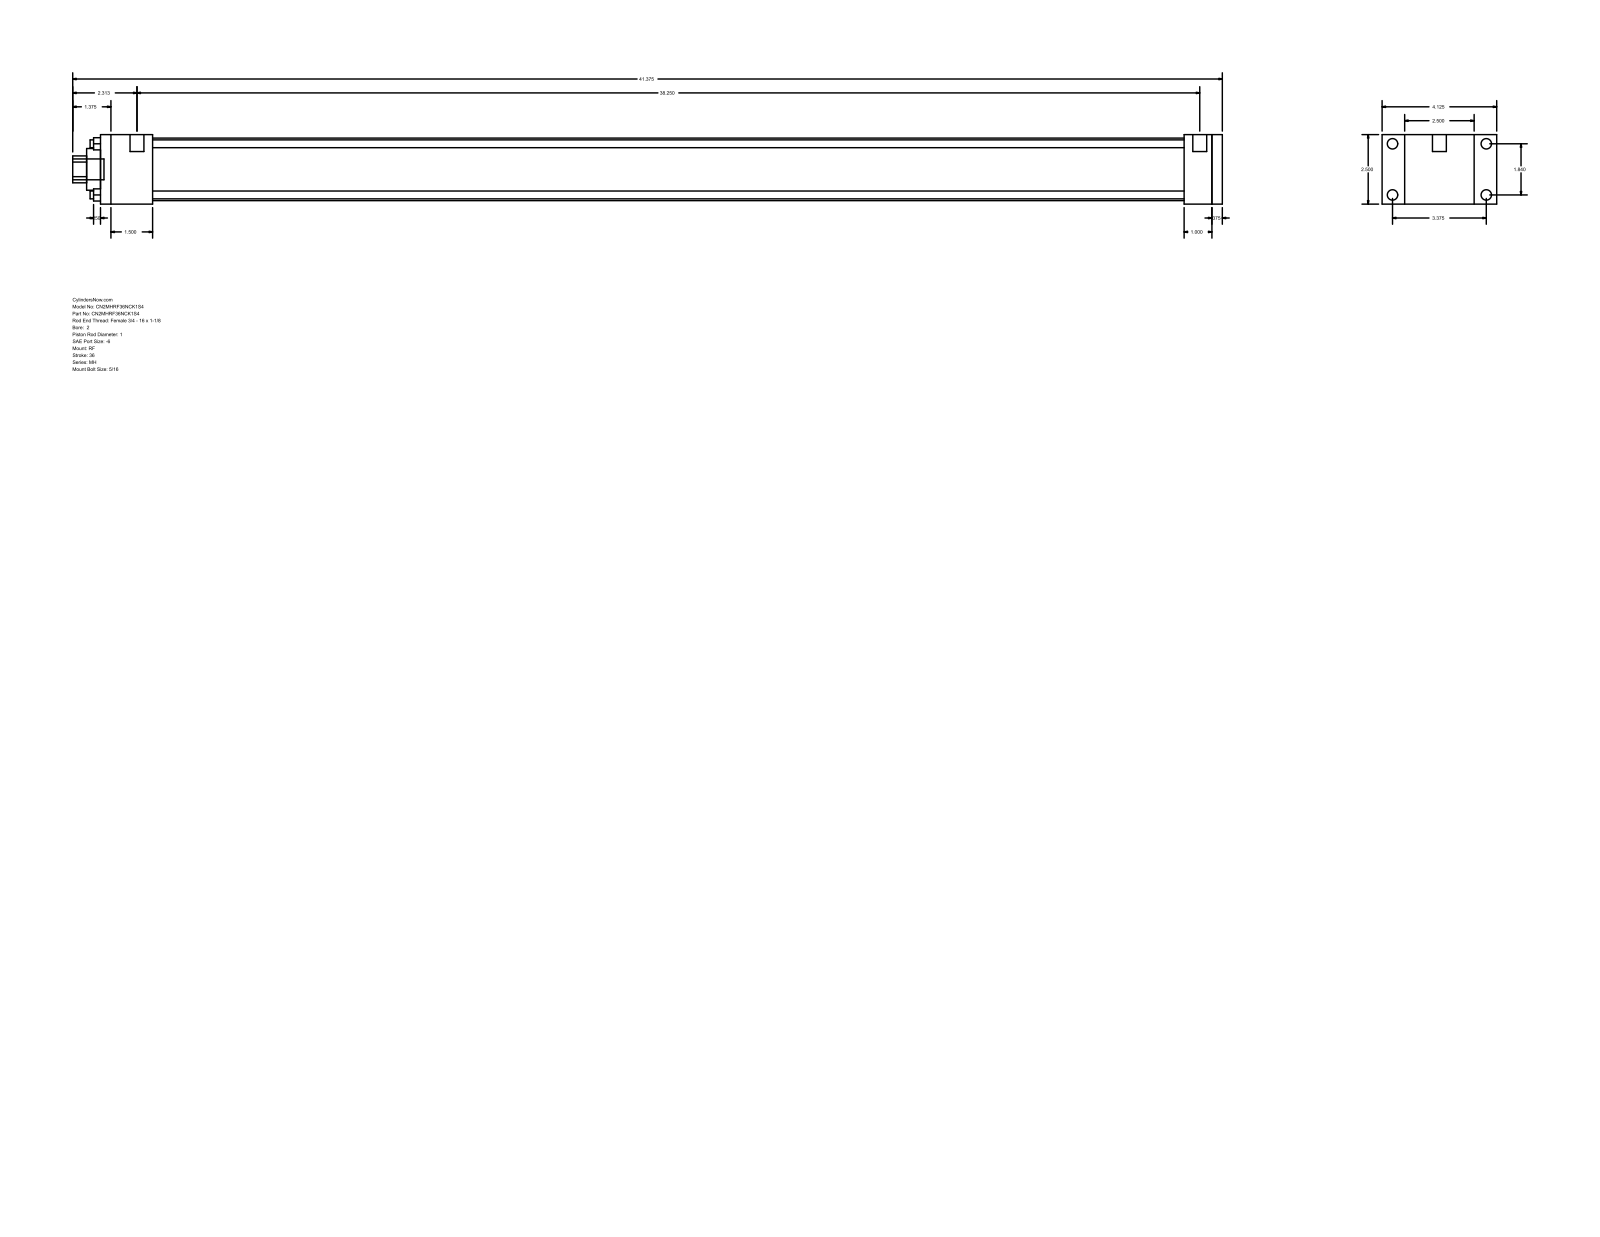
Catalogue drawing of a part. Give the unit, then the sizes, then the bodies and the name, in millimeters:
Units: millimetres
Overall size (bounding box): 1050.92 × 104.78 × 63.5
Round holes (diameter × count): ⌀7.14 ×4, ⌀25.4 ×1, ⌀38.1 ×1, ⌀57.15 ×1
Round bosses / shafts (diameter × count): ⌀9.53 ×4, ⌀5.56 ×4, ⌀12.7 ×2, ⌀19.05 ×1
Partial cylindrical surfaces — rounded edges, fillets, slot ends (radius × count): R12.29 ×1
Main face-to-face distances: 63.5, 9.52, 1025.52, 1016, 20.64, 25.4, 47.63, 990.6, 942.97, 968.37
Hole centre spacings: 33.05, 46.74, 66.1
Bodies: 0 solids, 92 faces (64 planar, 28 cylindrical, 0 other)
Part name (STEP PRODUCT): MH_RF__0200_1
STEP written by: GSSL Pune (CONFIG_CONTROL_DESIGN)
